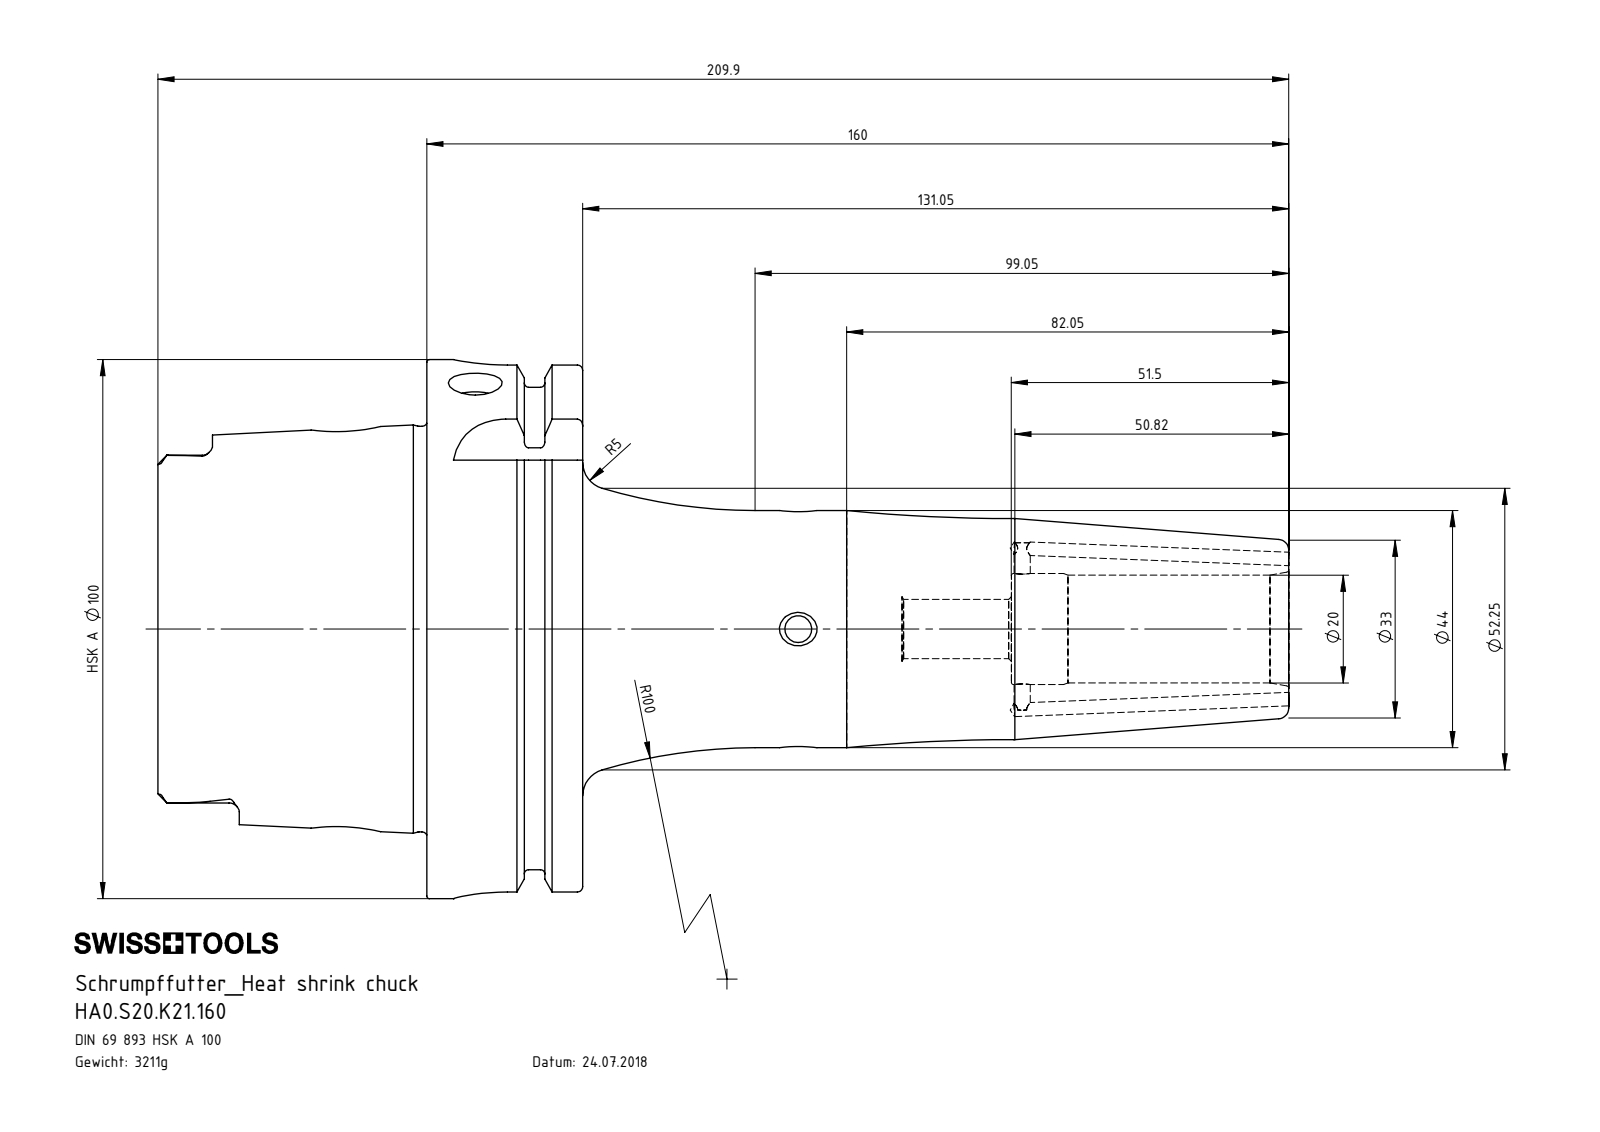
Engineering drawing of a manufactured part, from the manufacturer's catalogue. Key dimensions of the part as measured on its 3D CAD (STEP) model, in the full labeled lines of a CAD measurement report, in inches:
Part name (STEP PRODUCT): HA0-S20.K21.160_C_Fertigbearbeitung; ERU-AN5.K01.020_A; ERU-CJ2.001.006; HA0.S20.K21.160
STEP written by: SolidWorks 2017 (CONFIG_CONTROL_DESIGN)
Units: inches
Bodies: 4 solids, 307 faces (95 planar, 89 cylindrical, 123 other)
Overall size (bounding box): 8.267 × 3.937 × 3.937
Volume: 24.96 in³ · Surface area: 115.4 in²
Round holes (diameter × count): ⌀0.394 ×3, ⌀0.098 ×2, ⌀0.197 ×2, ⌀0.472 ×2, ⌀0.118 ×1, ⌀0.236 ×1, ⌀0.433 ×1, ⌀0.787 ×1, ⌀0.811 ×1, ⌀0.886 ×1, ⌀1.024 ×1, ⌀2.087 ×1
Round bosses / shafts (diameter × count): ⌀0.118 ×2, ⌀3.937 ×1, ⌀3.62 ×1, ⌀2.963 ×1, ⌀1.732 ×1, ⌀1.614 ×1
Partial cylindrical surfaces — rounded edges, fillets, slot ends (radius × count): R0.075 ×6, R0.192 ×4, R0.394 ×4
Main face-to-face distances: 1.14, 0.49, 0.65, 1.965, 2.455, 3.104, 3.457, 3.079, 1.114, 0.624
Hole centre spacings: 1.636, 2.439, 3.305, 4.941
